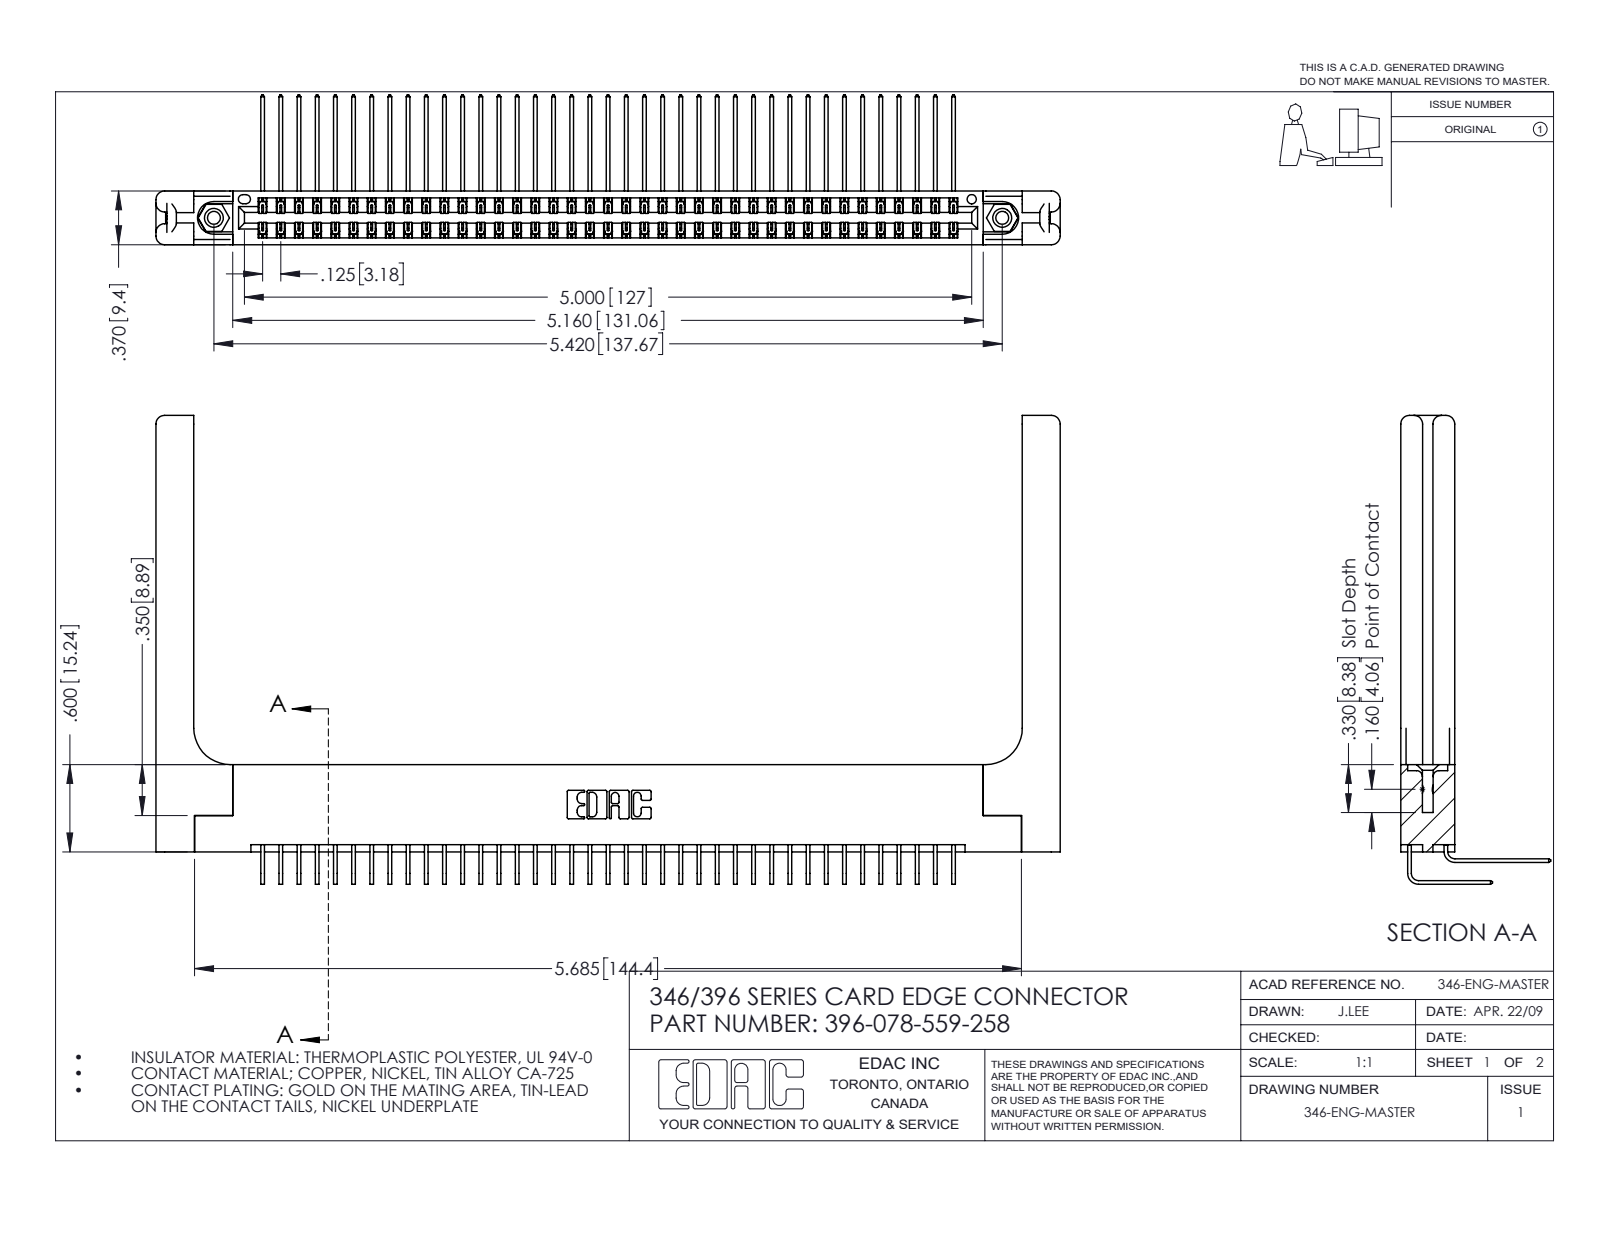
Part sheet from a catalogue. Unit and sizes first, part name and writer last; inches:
Units: inches
Overall size (bounding box): 6.216 × 3.223 × 1.03
Round holes (diameter × count): ⌀0.089 ×2, ⌀0.125 ×2, ⌀0.156 ×2, ⌀0.064 ×1
Round bosses / shafts (diameter × count): ⌀0.155 ×2
Partial cylindrical surfaces — rounded edges, fillets, slot ends (radius × count): R0.006 ×117, R0.01 ×22, R0.06 ×16, R0.007 ×6, R0.031 ×6, R0.026 ×3, R0.014 ×2, R0.022 ×2
Main face-to-face distances: 0.048, 0.322, 0.37, 0.072, 0.025, 0.148, 0.15, 0.25, 0.298, 0.275
Hole centre spacings: 0.246, 5.211, 5.42
Volume: 1.423 in³ · Surface area: 44.69 in²
Bodies: 83 solids, 4590 faces (3110 planar, 1420 cylindrical, 60 other)
Part name (STEP PRODUCT): 346-220-058_345-220-058; 345-292-001_559 Tail - 2; 345-292-001_558 559 Tail - 1; 346 Part_Flush Mounting Lugs - 0.156 Dia-TH (+2 more)
STEP written by: SolidWorks 2016 (CONFIG_CONTROL_DESIGN)
